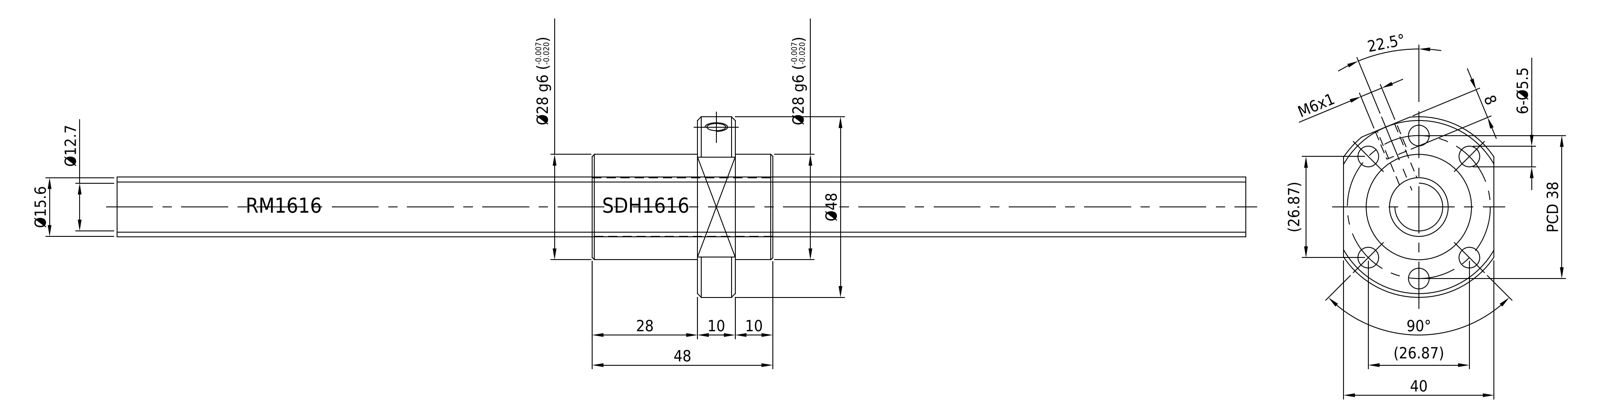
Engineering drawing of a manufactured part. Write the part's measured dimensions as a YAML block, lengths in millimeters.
part_name: "RM1616; SDH1616"
step_written_by: "SolidWorks 2013 (CONFIG_CONTROL_DESIGN)"
units: millimeters
bodies: {solids: 2, faces: 50, planar: 9, cylindrical: 27, other: 14}
overall_size: [300, 48, 40]
volume: 88155
surface_area: 26383
round_holes:
  - {diameter: 5.5, count: 6}
  - {diameter: 3, count: 1}
  - {diameter: 5, count: 1}
  - {diameter: 16, count: 1}
round_bosses_or_shafts:
  - {diameter: 28, count: 1}
  - {diameter: 15.9, count: 1}
partial_cylinders:
  - {radius: 24, count: 1}
face_to_face_distances: [10, 126, 174, 20, 48, 38, 28, 40, 136, 146]
hole_center_spacings: [19, 26.87, 14.54, 38, 35.1, 35.11, 14.55, 18.99]
